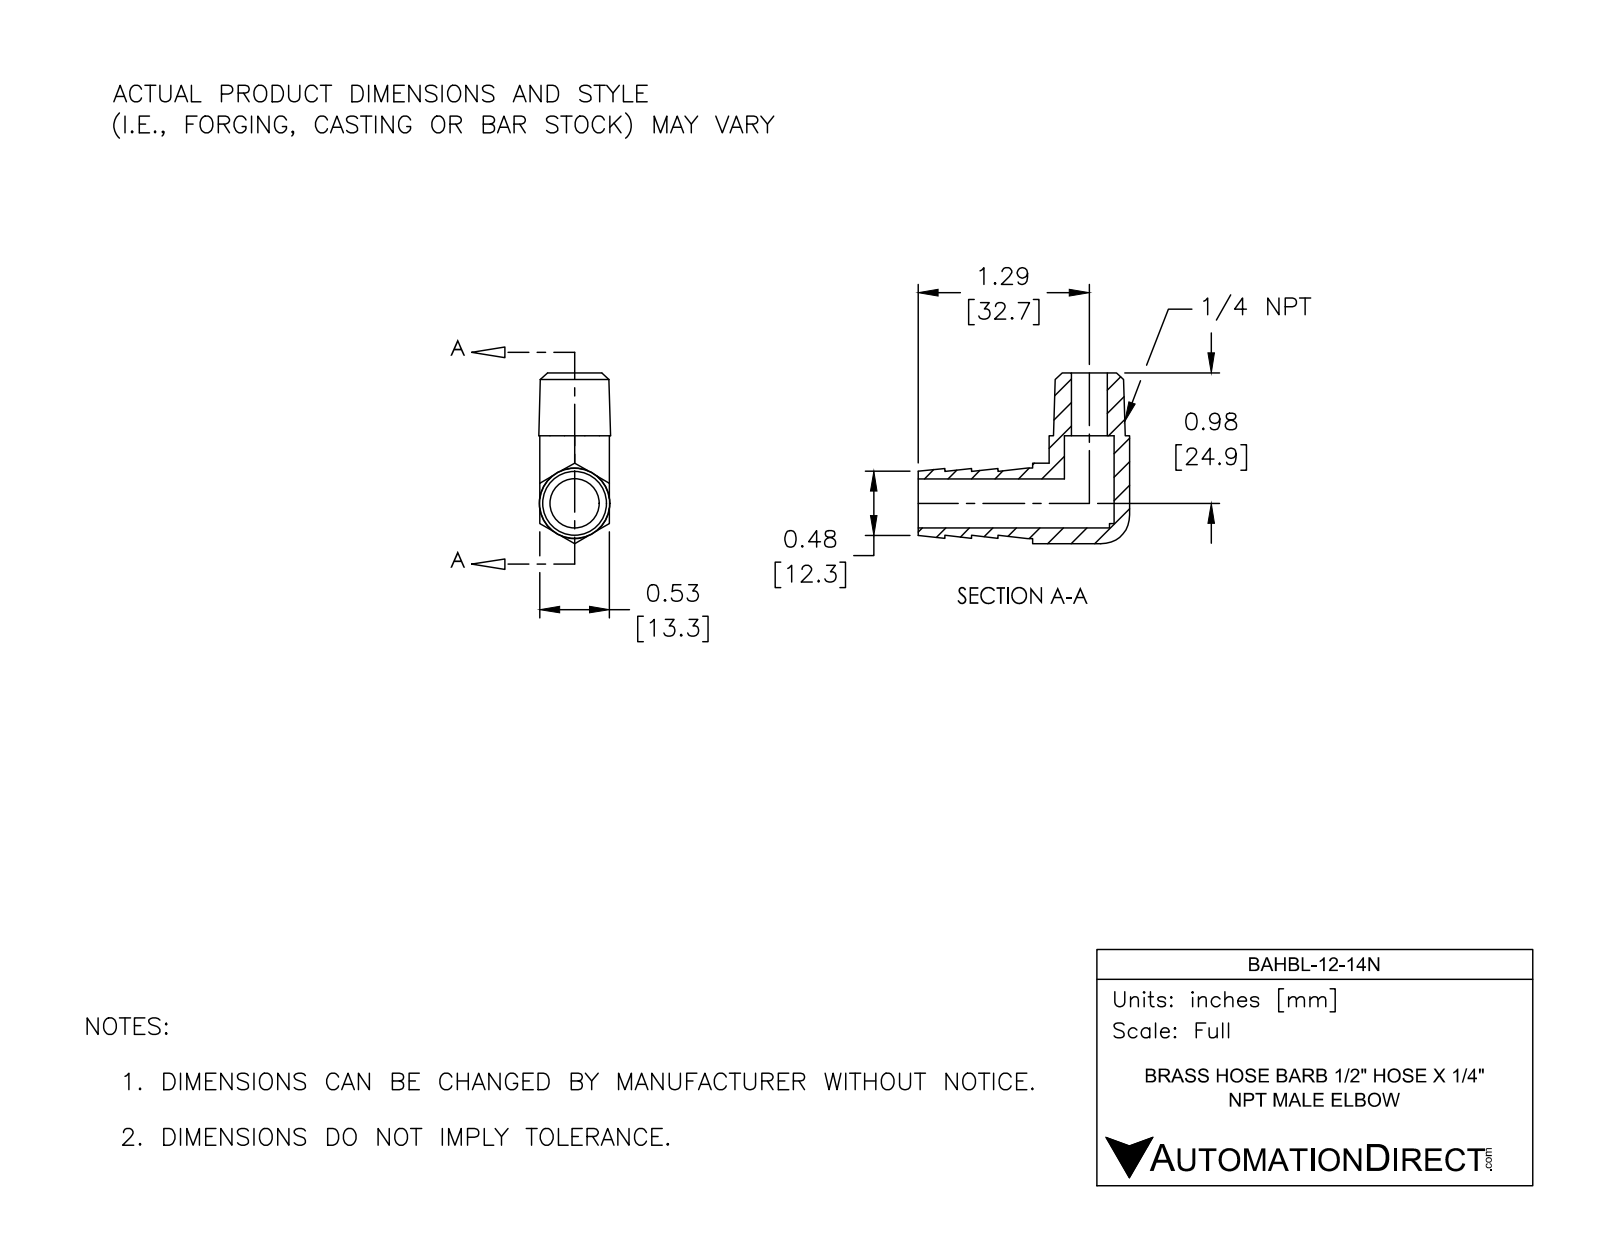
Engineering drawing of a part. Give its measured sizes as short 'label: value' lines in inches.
name: BAHBL-12-14N
written by: SolidWorks 2017 (AUTOMOTIVE_DESIGN)
unit: in
bodies: 1 solid, 69 faces (44 planar, 13 cylindrical, 12 other)
size: 1.59 × 1.285 × 0.54
volume: 0.269 in³; area: 6.708 in²
holes: 1× ⌀0.27, 1× ⌀0.369, 1× ⌀0.374
bosses: 1× ⌀0.531
rounds: 2× R0.25
face distances: 0.525, 0.525, 0.2, 0.4, 0.474, 0.659, 1.133, 0.6, 0.839, 1.039
